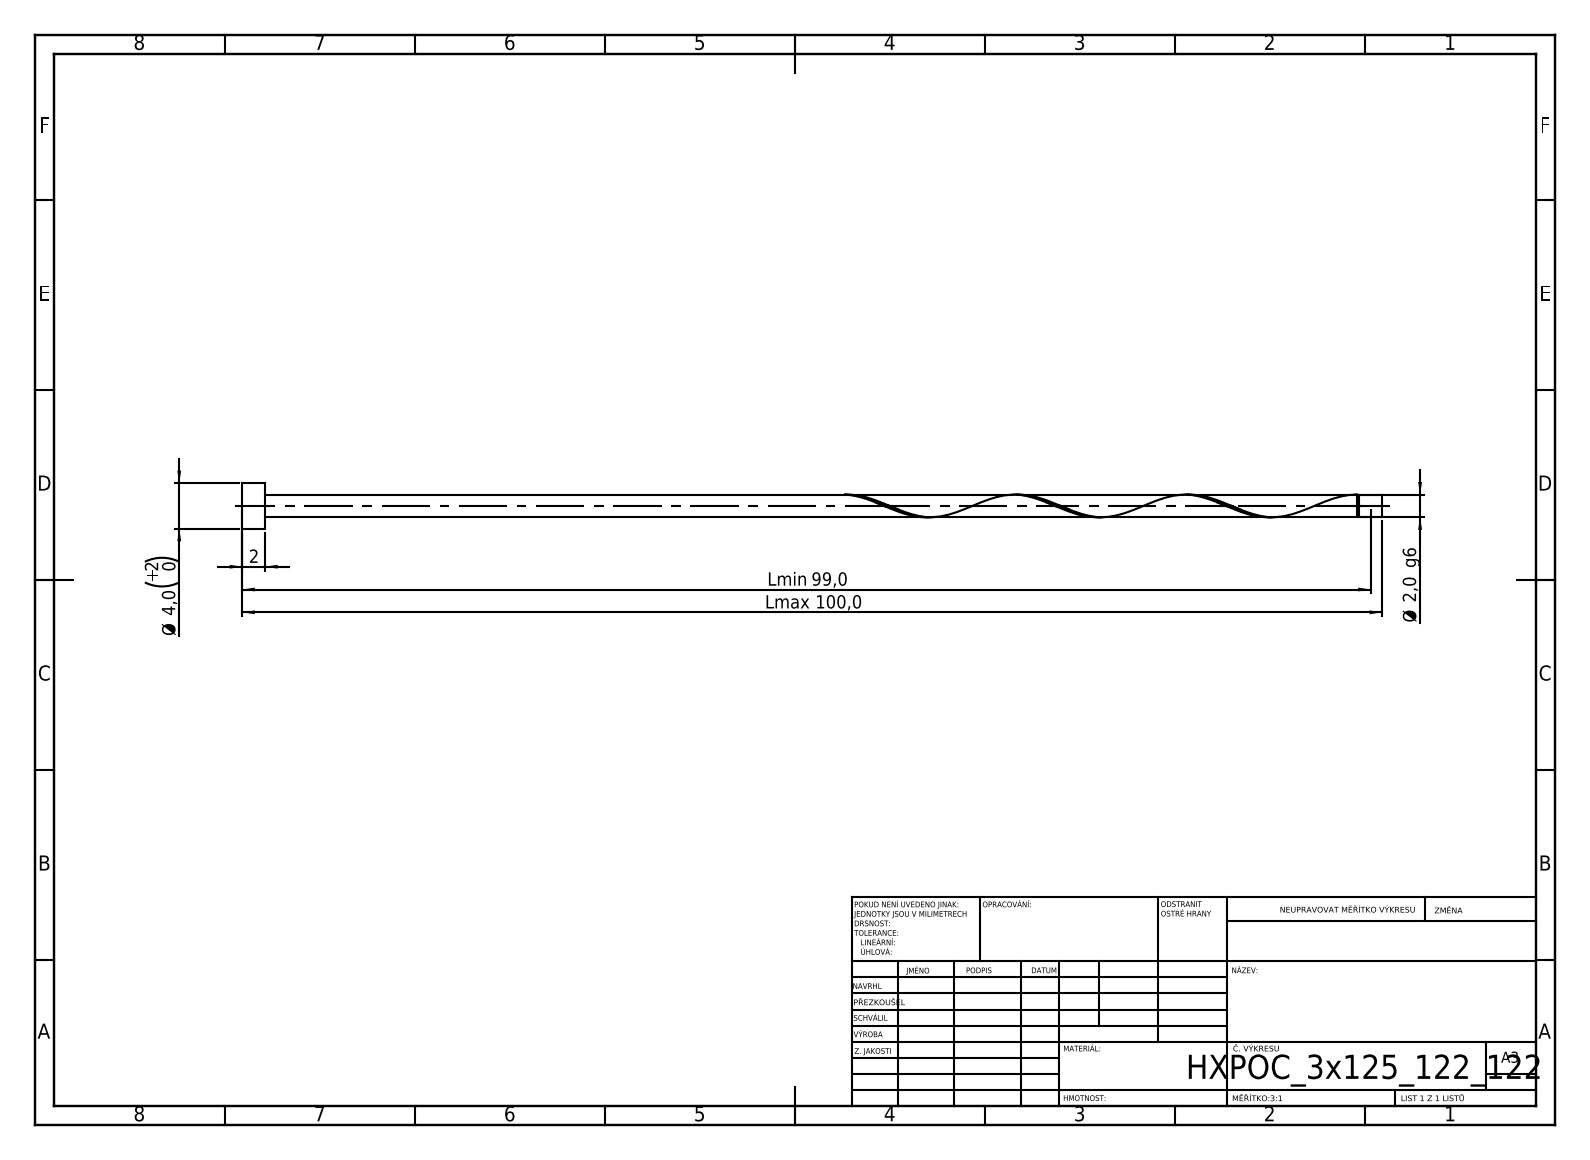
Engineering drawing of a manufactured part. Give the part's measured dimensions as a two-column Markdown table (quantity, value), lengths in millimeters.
| quantity | value |
| --- | --- |
| STEP written by | SolidWorks 2019 (CONFIG_CONTROL_DESIGN) |
| units | millimeters |
| bodies | 1 solid, 21 faces (6 planar, 14 cylindrical, 1 other) |
| overall size | 100 × 4 × 4 |
| volume | 332 mm³ |
| surface area | 672 mm² |
| round bosses / shafts (diameter × count) | 4 × 1, 2 × 1, 1.8 × 1 |
| main face-to-face distances | 2, 98, 100, 96, 97.8, 95.8, 2.2, 52.8, 50.8, 45 |
